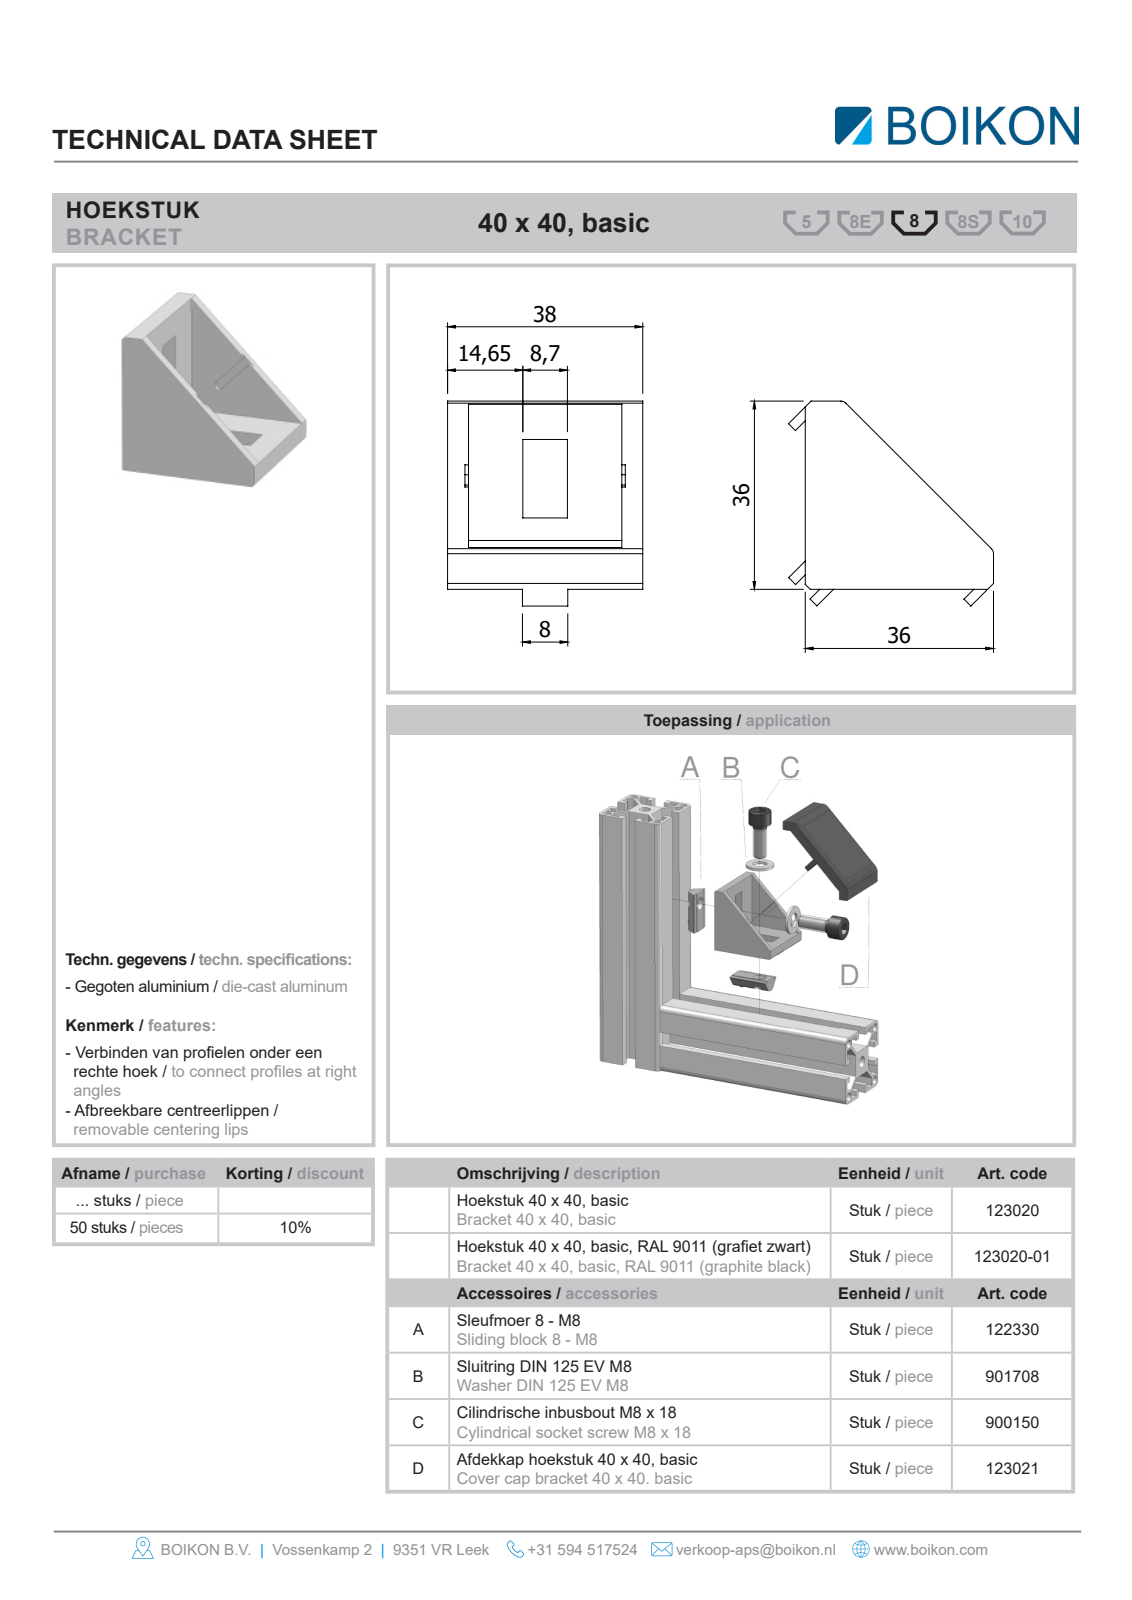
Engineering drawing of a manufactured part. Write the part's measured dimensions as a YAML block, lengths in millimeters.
part_name: "Root; 123020HOEKSTUK 40X40 BASICBOIKON; 123021AFDEKKAP HOEKSTUK 40X40 BASICBOIKON; 122330Sleufmoer 8 - M8 met kogelBOIKON (+2 more)"
step_written_by: "HiCAD 2013 1802.4 Build 509 (AUTOMOTIVE_DESIGN)"
units: millimeters
bodies: {solids: 8, faces: 255, planar: 206, cylindrical: 41, other: 8}
overall_size: [53.12, 53.12, 38]
volume: 26939
surface_area: 20051
round_holes:
  - {diameter: 8, count: 2}
  - {diameter: 8.4, count: 2}
round_bosses_or_shafts:
  - {diameter: 16, count: 2}
  - {diameter: 13, count: 2}
  - {diameter: 6.47, count: 2}
partial_cylinders:
  - {radius: 2, count: 6}
  - {radius: 0.5, count: 4}
  - {radius: 1, count: 3}
  - {radius: 4, count: 2}
  - {radius: 5, count: 2}
  - {radius: 7, count: 2}
  - {radius: 1.1, count: 1}
face_to_face_distances: [3, 0.5, 5.5, 34.5, 2.5, 35, 7, 4, 38, 3.5]
